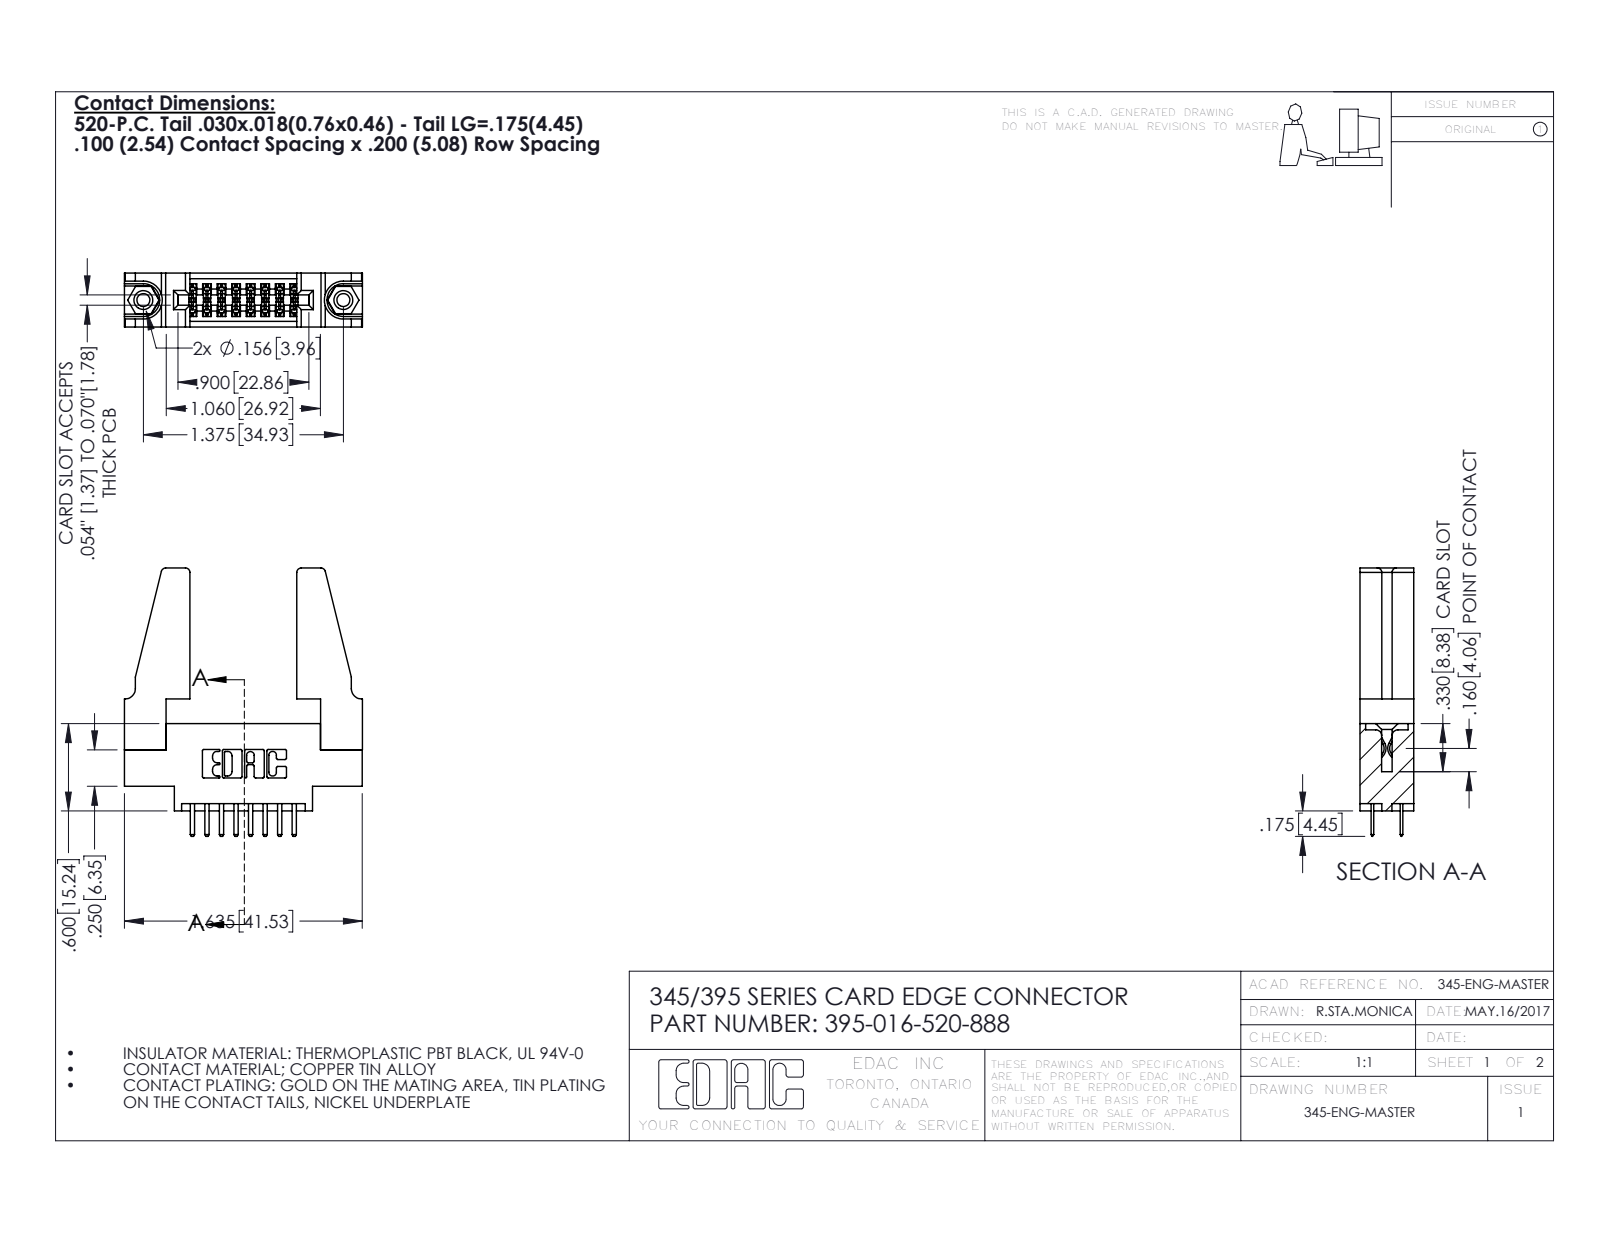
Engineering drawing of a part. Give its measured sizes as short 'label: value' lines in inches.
name: 395-016-520-888; 345-292-001_345-293-120; 345-220-078_345-220-088; 345 Part_0.170 Offset - 0.156 Dia-TH (+1 more)
written by: SolidWorks 2016 (CONFIG_CONTROL_DESIGN)
unit: in
bodies: 21 solids, 1118 faces (716 planar, 386 cylindrical, 16 other)
size: 1.845 × 1.636 × 0.37
volume: 0.418 in³; area: 12.27 in²
holes: 2× ⌀0.089, 2× ⌀0.125, 2× ⌀0.156, 1× ⌀0.064
bosses: 2× ⌀0.155
rounds: 24× R0.006, 22× R0.01, 20× R0.01, 8× R0.03, 6× R0.007, 6× R0.031, 3× R0.026, 2× R0.014
face distances: 0.37, 0.072, 0.298, 0.2, 0.225, 0.098, 0.272, 0.025, 0.148, 0.15
hole spacings: 0.27, 1.144, 1.375
